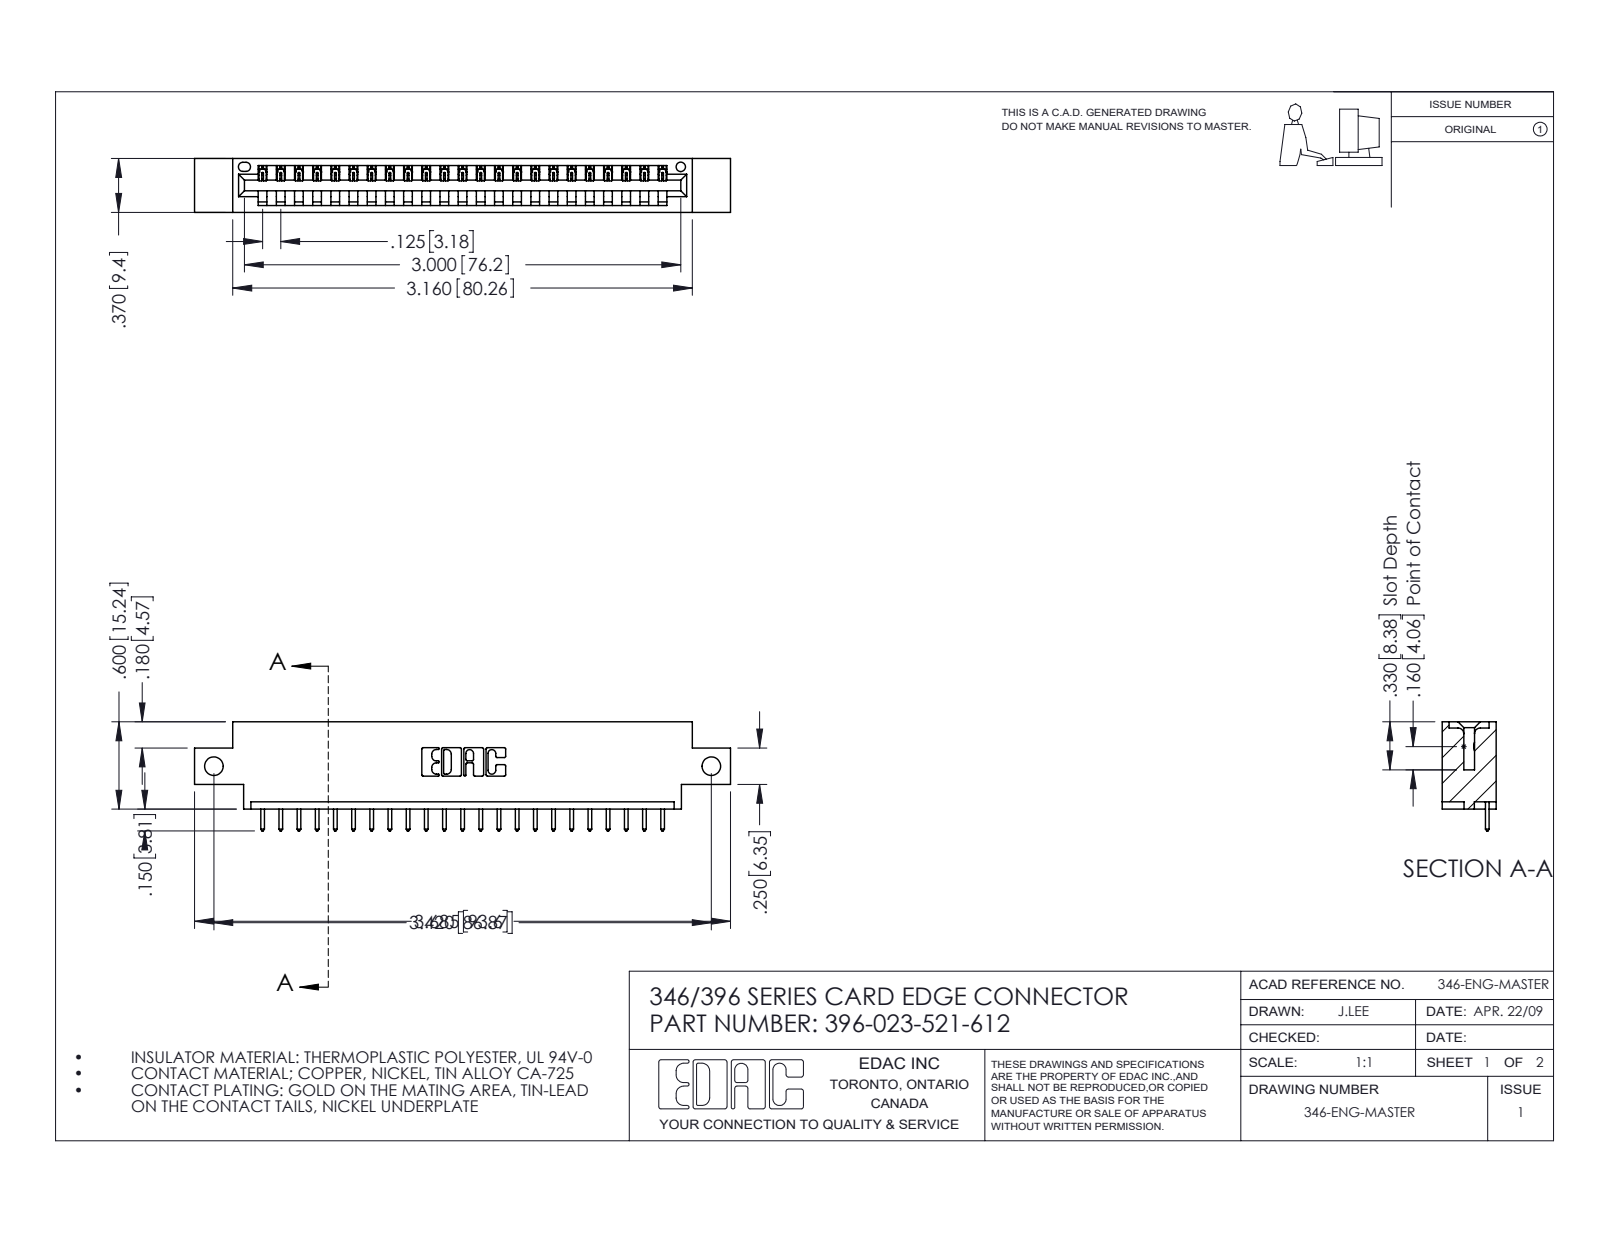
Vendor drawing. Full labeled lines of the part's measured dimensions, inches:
Part name (STEP PRODUCT): 345-292-001_345-293-121; 346 Part_0.170 Offset - Side Mount; 396-023-521-612
STEP written by: SolidWorks 2016 (CONFIG_CONTROL_DESIGN)
Units: inches
Bodies: 24 solids, 1460 faces (1000 planar, 460 cylindrical, 0 other)
Overall size (bounding box): 3.685 × 0.75 × 0.37
Volume: 0.52 in³ · Surface area: 15.81 in²
Round holes (diameter × count): ⌀0.128 ×2, ⌀0.064 ×1
Partial cylindrical surfaces — rounded edges, fillets, slot ends (radius × count): R0.006 ×46, R0.01 ×46, R0.01 ×22, R0.007 ×6, R0.031 ×6, R0.026 ×3, R0.031 ×2, R0.04 ×2
Main face-to-face distances: 0.048, 0.322, 0.37, 0.25, 0.072, 0.298, 0.025, 0.148, 0.222, 0.1
Hole centre spacings: 3.42
